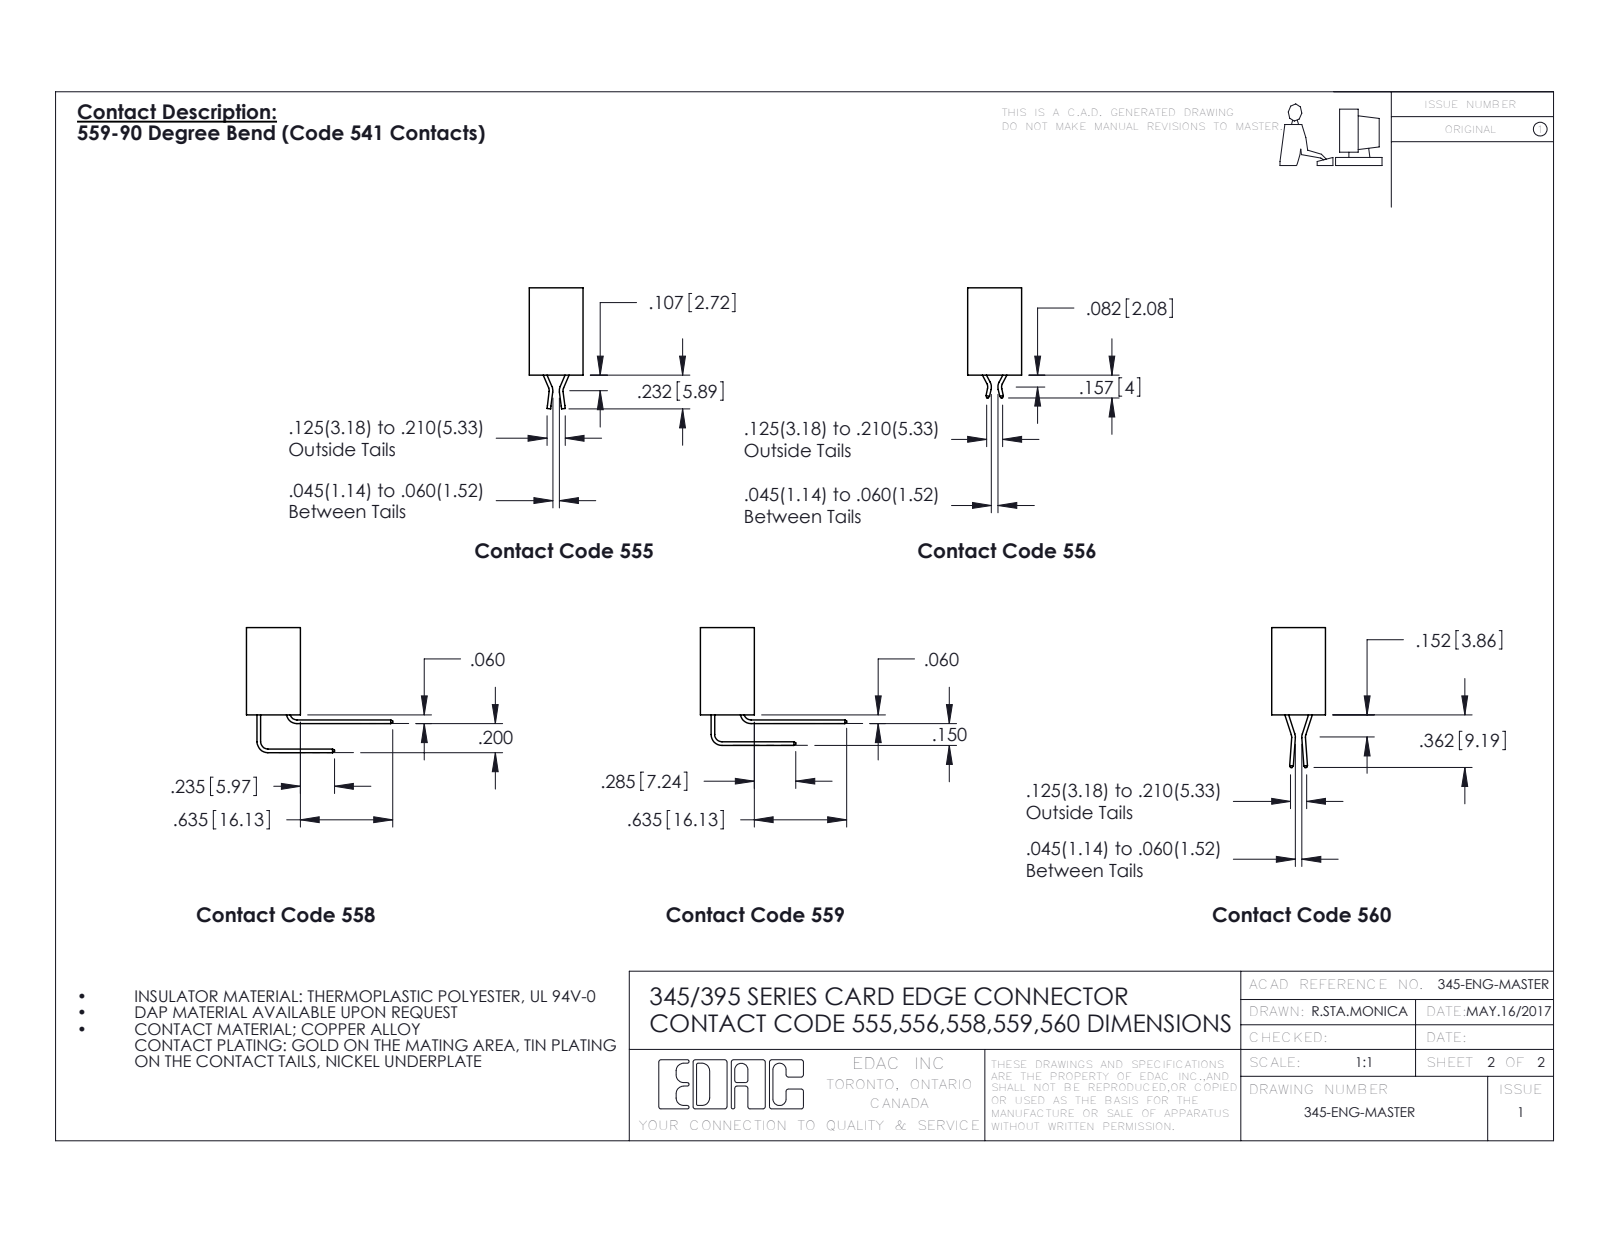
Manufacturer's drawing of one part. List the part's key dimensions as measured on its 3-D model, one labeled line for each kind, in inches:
Part name (STEP PRODUCT): 345-292-001_345-293-124; 345 Part_No Mounting Lugs; 395-064-524-201
STEP written by: SolidWorks 2016 (CONFIG_CONTROL_DESIGN)
Units: inches
Bodies: 65 solids, 3574 faces (2572 planar, 1002 cylindrical, 0 other)
Overall size (bounding box): 3.46 × 0.762 × 0.37
Volume: 0.547 in³ · Surface area: 20.31 in²
Round holes (diameter × count): ⌀0.064 ×1
Partial cylindrical surfaces — rounded edges, fillets, slot ends (radius × count): R0.006 ×96, R0.01 ×22, R0.007 ×6, R0.031 ×6, R0.026 ×3, R0.014 ×2, R0.019 ×2, R0.022 ×2
Main face-to-face distances: 0.298, 0.072, 0.2, 0.37, 0.098, 0.272, 0.025, 0.225, 0.072, 0.175
